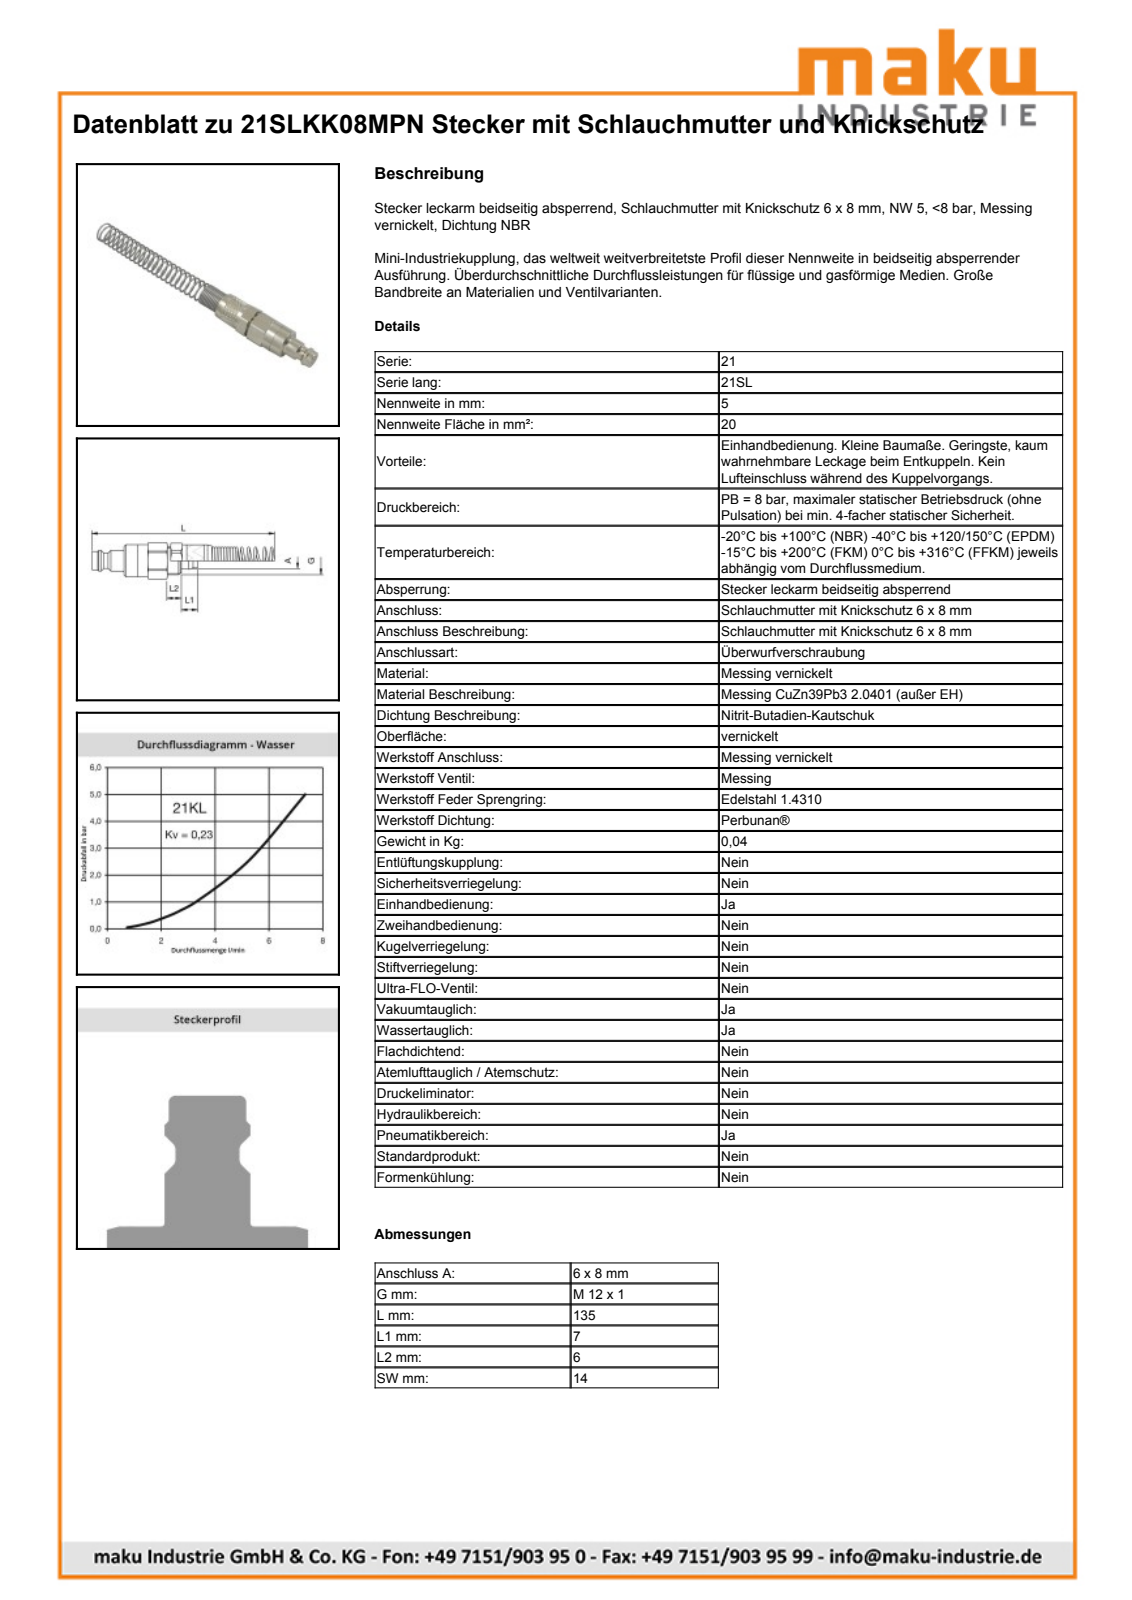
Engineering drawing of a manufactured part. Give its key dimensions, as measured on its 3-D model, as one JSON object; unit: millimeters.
{"part_name": "D110838", "step_written_by": "Autodesk Inventor 2013 (AUTOMOTIVE_DESIGN)", "units": "millimeters", "bodies": {"solids": 2, "faces": 108, "planar": 28, "cylindrical": 31, "other": 49}, "overall_size": [132.64, 15.72, 14.88], "volume_mm3": 6385, "surface_area_mm2": 7384, "round_holes": [[8.25, 1], [12, 1]], "round_bosses_or_shafts": [[14, 1], [13.5, 1], [13.4, 1], [11.98, 1], [11, 1], [10.95, 1], [10.6, 1], [9, 1]], "partial_cylinders_radius": [[7.7, 1], [7.9, 1]], "face_to_face_distances": [14, 24.75, 14.1, 38.85, 39.75, 25.65, 0.9, 45.95, 31.85, 7.1]}
